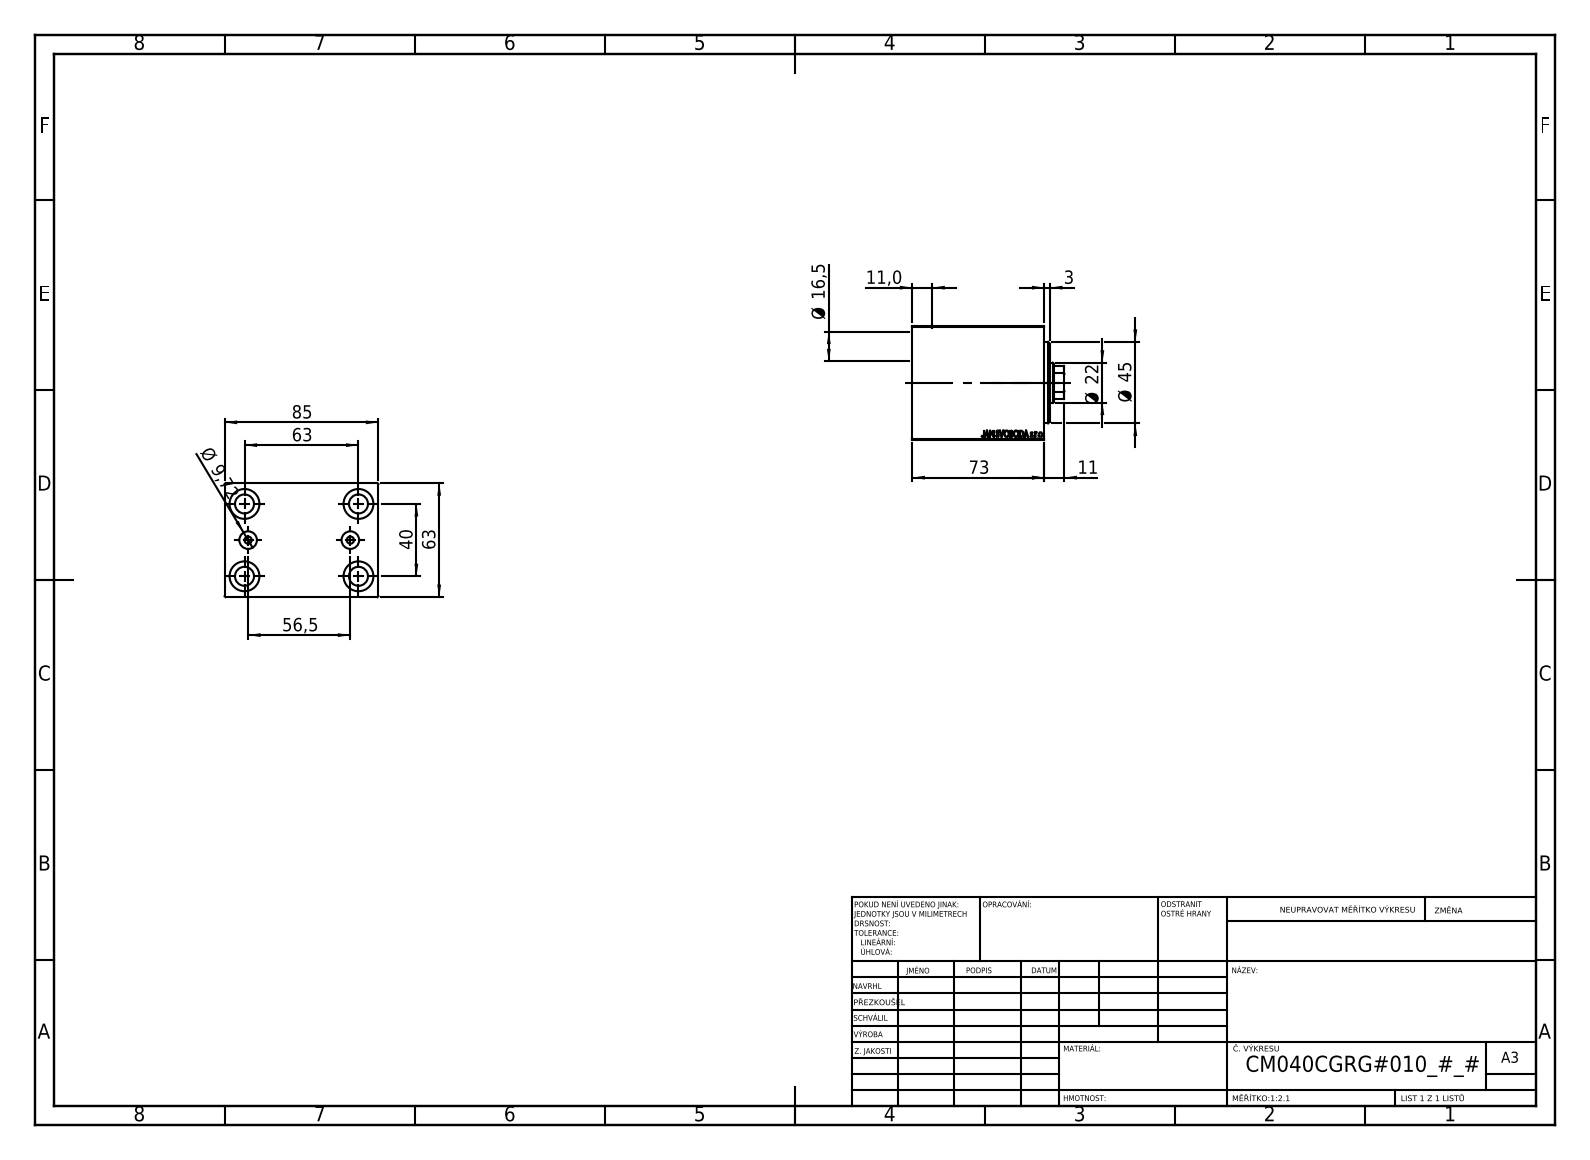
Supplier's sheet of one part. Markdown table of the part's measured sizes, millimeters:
| quantity | value |
| --- | --- |
| part name | V450CM_C_VCP; V450CM_VC_B; V450CM_C_Body |
| STEP written by | SolidWorks 2019 (CONFIG_CONTROL_DESIGN) |
| units | millimeters |
| bodies | 3 solids, 858 faces (408 planar, 56 cylindrical, 394 other) |
| overall size | 85 × 84 × 63 |
| volume | 347 181 mm³ |
| surface area | 67 532 mm² |
| round holes (diameter × count) | 10.5 × 4, 16.5 × 4, 4 × 2, 9.72 × 2, 12.5 × 1, 22 × 1, 25.5 × 1, 40 × 1, 42 × 1, 45 × 1 |
| partial cylindrical surfaces (radius × count) | 10.5 × 1 |
| main face-to-face distances | 63, 85, 51, 73, 22, 11, 62, 21.6, 29.4, 51.4 |
| hole center spacings | 37.31, 20.1, 20.5, 40, 61.82, 63, 64.2, 74.63 |
